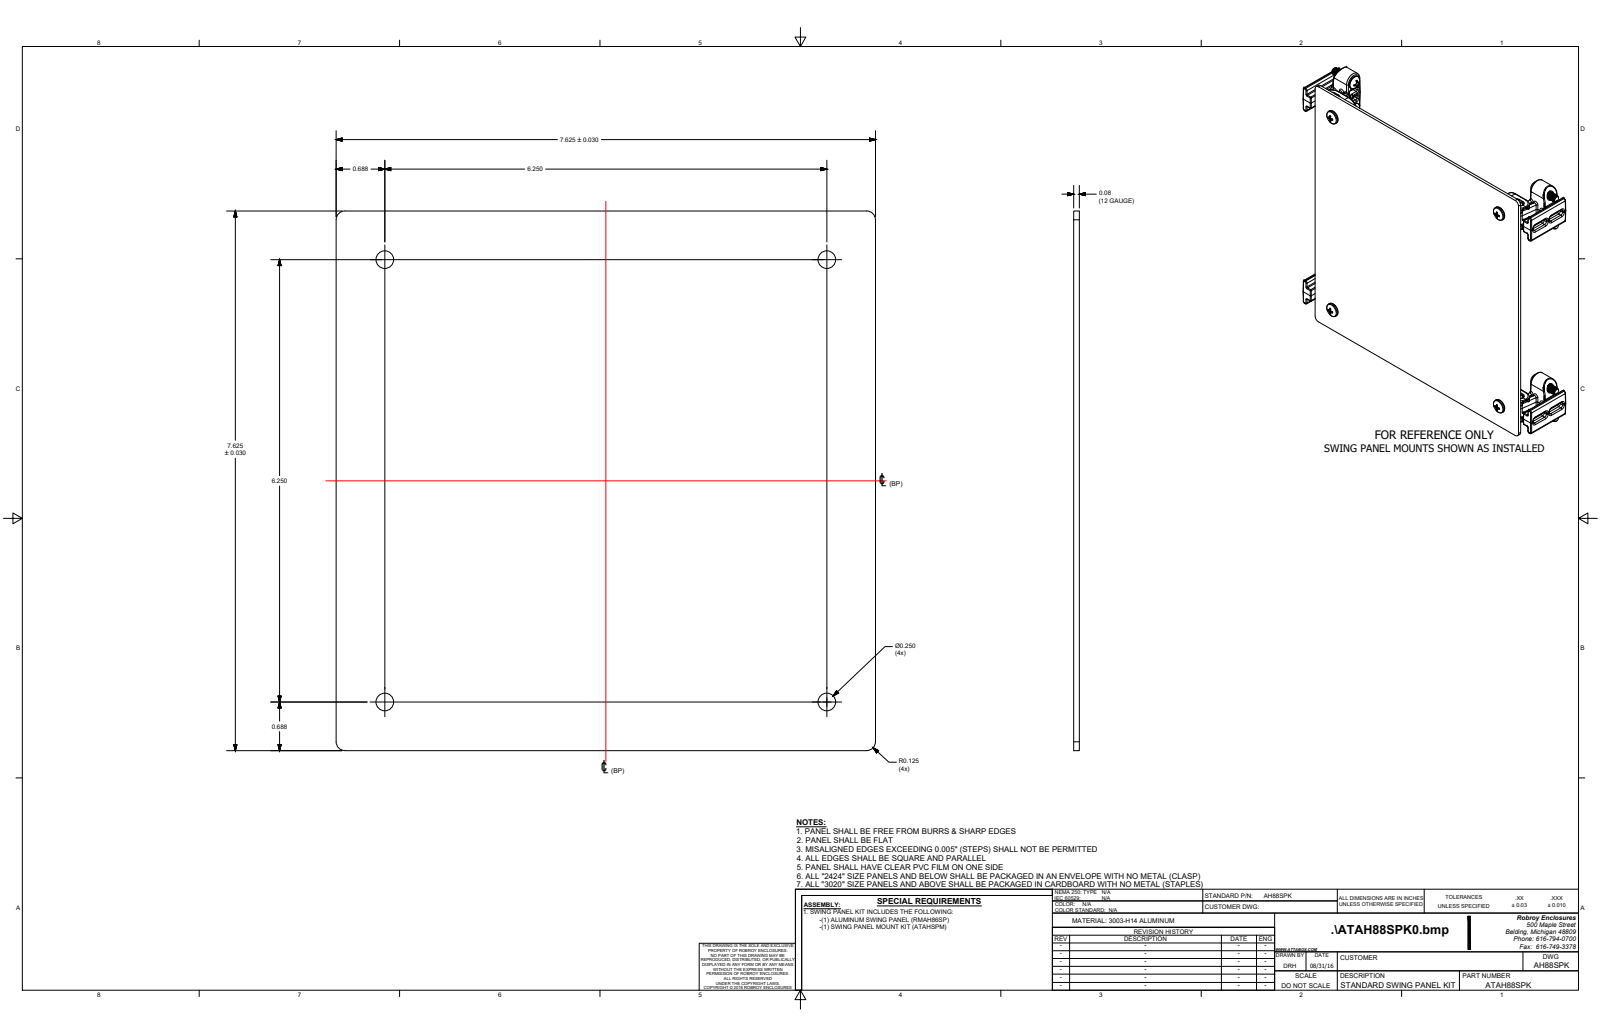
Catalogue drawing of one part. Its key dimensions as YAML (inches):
part_name: "AH88SPK"
step_written_by: "SolidWorks 2019 (AUTOMOTIVE_DESIGN)"
units: inches
bodies: {solids: 33, faces: 2010, planar: 518, cylindrical: 736, other: 756}
overall_size: [8.559, 7.625, 1.448]
volume: 7.722
surface_area: 176
round_holes:
  - {diameter: 0.156, count: 8}
  - {diameter: 0.25, count: 8}
round_bosses_or_shafts:
  - {diameter: 0.373, count: 8}
  - {diameter: 0.262, count: 8}
  - {diameter: 0.19, count: 8}
partial_cylinders:
  - {radius: 0.035, count: 248}
  - {radius: 0.02, count: 124}
  - {radius: 0.065, count: 54}
  - {radius: 0.015, count: 30}
  - {radius: 0.045, count: 16}
  - {radius: 0.05, count: 16}
  - {radius: 0.025, count: 14}
  - {radius: 0.9, count: 8}
face_to_face_distances: [0.08, 0.106, 6.25, 0.5, 0.51, 0.59, 0.3, 8.559, 8.259, 7.697]
hole_center_spacings: [6.25, 0.875, 6.25, 8.839, 5.375, 7.125]
